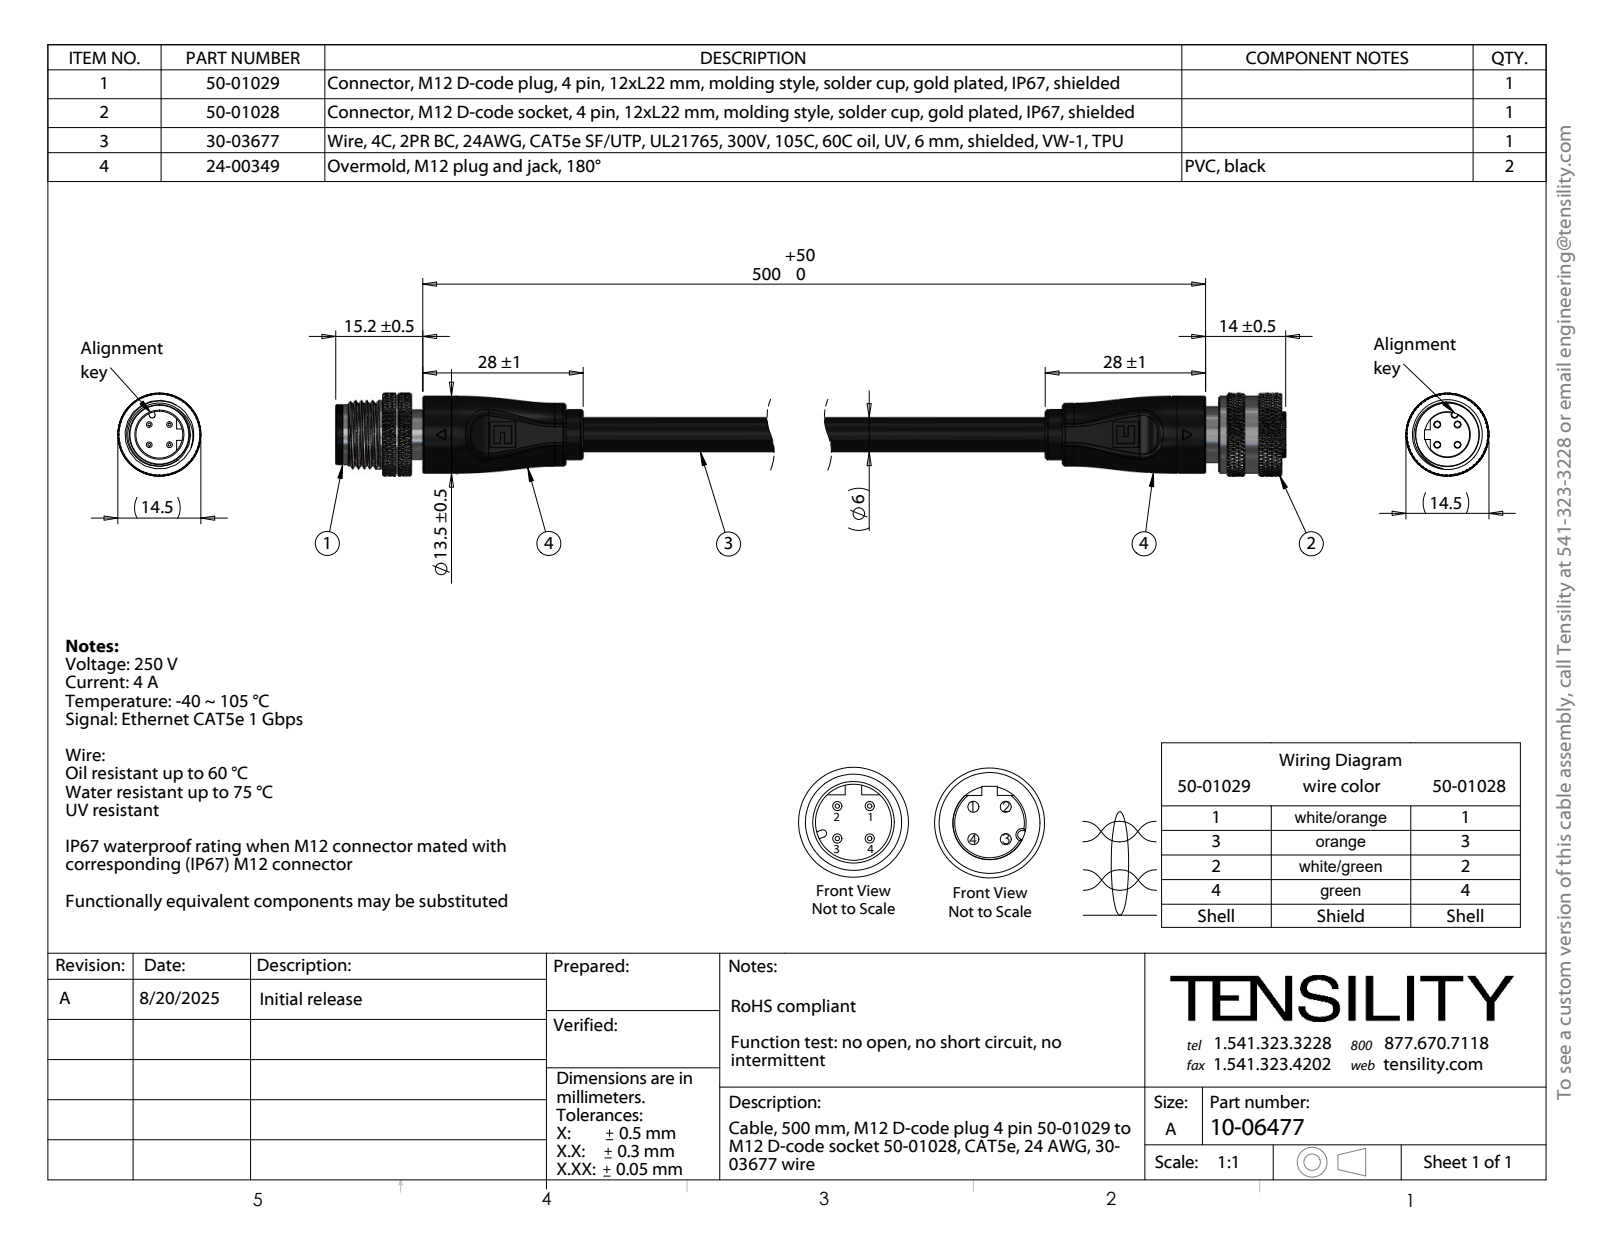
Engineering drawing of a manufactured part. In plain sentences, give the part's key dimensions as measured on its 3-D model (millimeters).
The part is named "50-01029-03_默认; 50-01028-02_默认; 50-01029-04_默认; 10-06477 (+8 more)". Its 3-D file was written by "SolidWorks 2025 (CONFIG_CONTROL_DESIGN)". It is 53 solids with 5792 faces: 362 planar, 1477 cylindrical and 3953 other. Overall it measures 235.2 by 14.5 by 14.5 millimeters. Its volume is 13 734 cubic millimeters and its surface area 30 639 square millimeters. Round holes: 28 of diameter 0.2, 4 of diameter 1, 4 of diameter 1.05, 4 of diameter 1.1, 4 of diameter 1.2, 1 of diameter 3.16, 1 of diameter 3.21, 1 of diameter 3.56, 1 of diameter 8.2, 1 of diameter 9.5, 1 of diameter 10, 1 of diameter 11.2. Round bosses or shafts: 4 of diameter 1.6, 4 of diameter 1.5, 4 of diameter 1.4, 1 of diameter 14.5, 1 of diameter 13.9, 1 of diameter 13.5, 1 of diameter 12, 1 of diameter 11. Partial cylindrical surfaces (rounded edges, fillets, slot ends): 10 of radius 0.1, 6 of radius 0.4, 4 of radius 0.5, 2 of radius 1.5, 2 of radius 1.96, 2 of radius 5, 1 of radius 5.58, 1 of radius 6.75. The main face-to-face distances are 206, 7, 28, 178, 2, 208, 3.8, 211.8, 208.3, 5.8. The hole center spacings are 1.91, 0.36, 2.09, 1.06, 0.89, 1.08, 1.24, 1.8.
